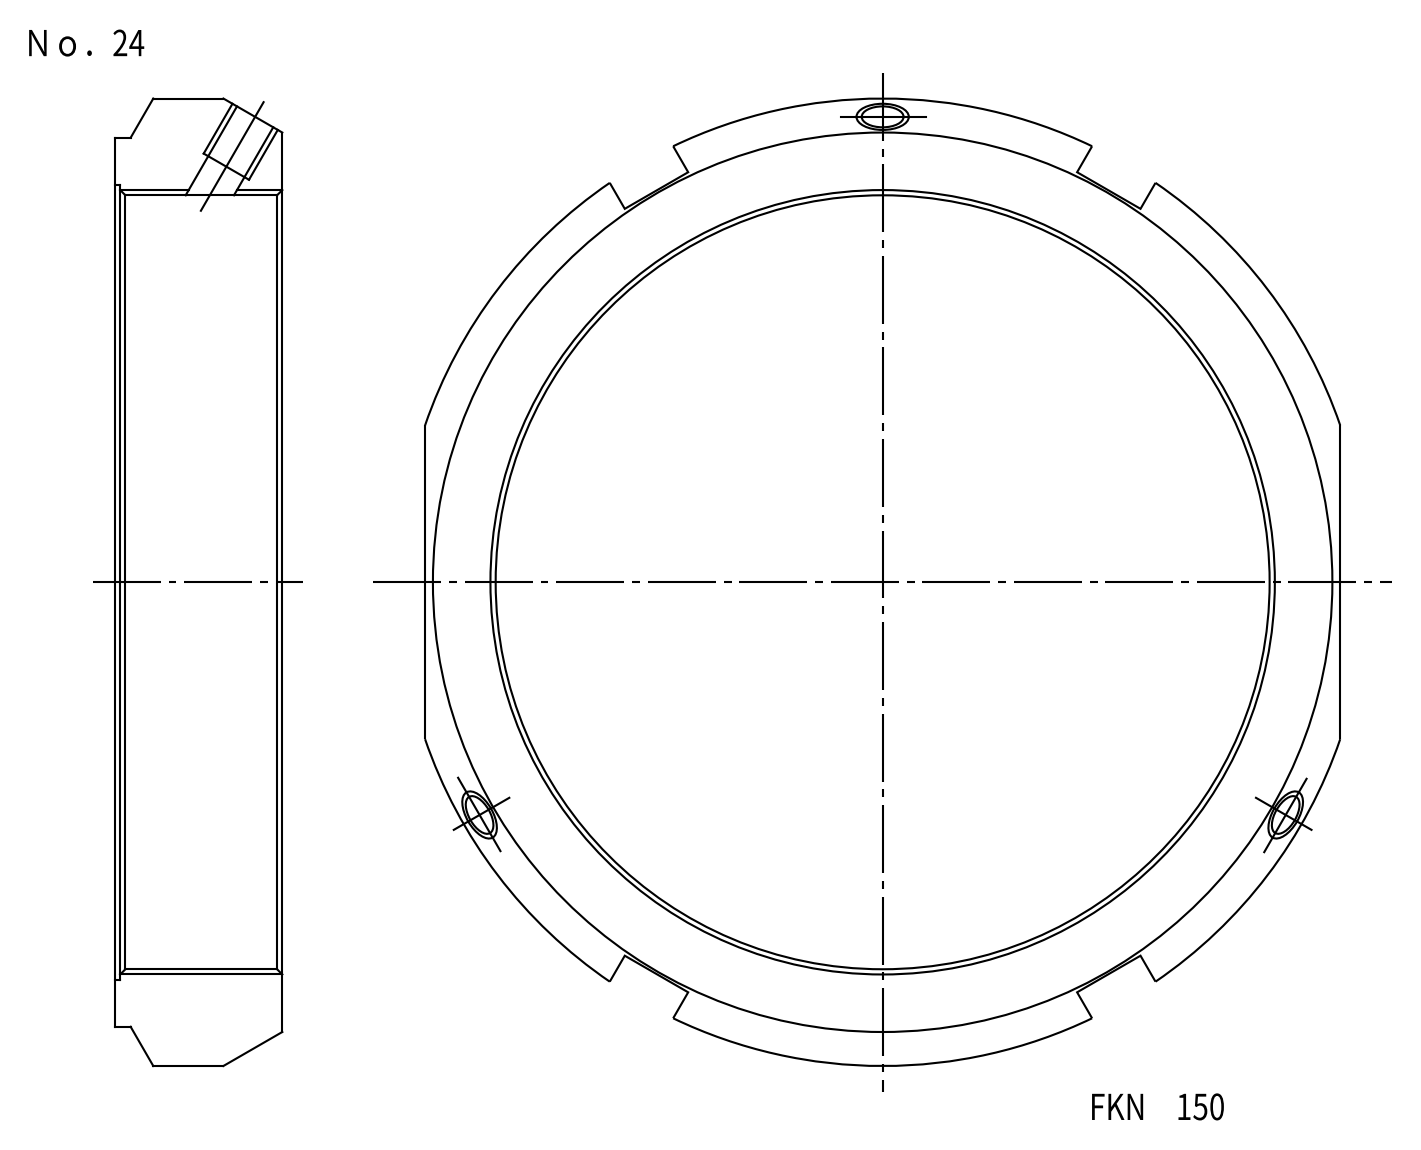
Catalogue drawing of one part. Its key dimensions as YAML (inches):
part_name: "FKD FKN150"
step_written_by: "Autodesk Inventor LT (CONFIG_CONTROL_DESIGN)"
units: inches
bodies: {solids: 1, faces: 37, planar: 20, cylindrical: 15, other: 2}
overall_size: [7.283, 6.89, 1.26]
volume: 14.33
surface_area: 74.99
round_holes:
  - {diameter: 0.33, count: 3}
  - {diameter: 0.402, count: 3}
  - {diameter: 5.906, count: 1}
  - {diameter: 5.984, count: 1}
round_bosses_or_shafts:
  - {diameter: 6.693, count: 1}
partial_cylinders:
  - {radius: 3.642, count: 1}
face_to_face_distances: [1.26, 6.89, 6.811, 0.059, 1.201, 0.551]
